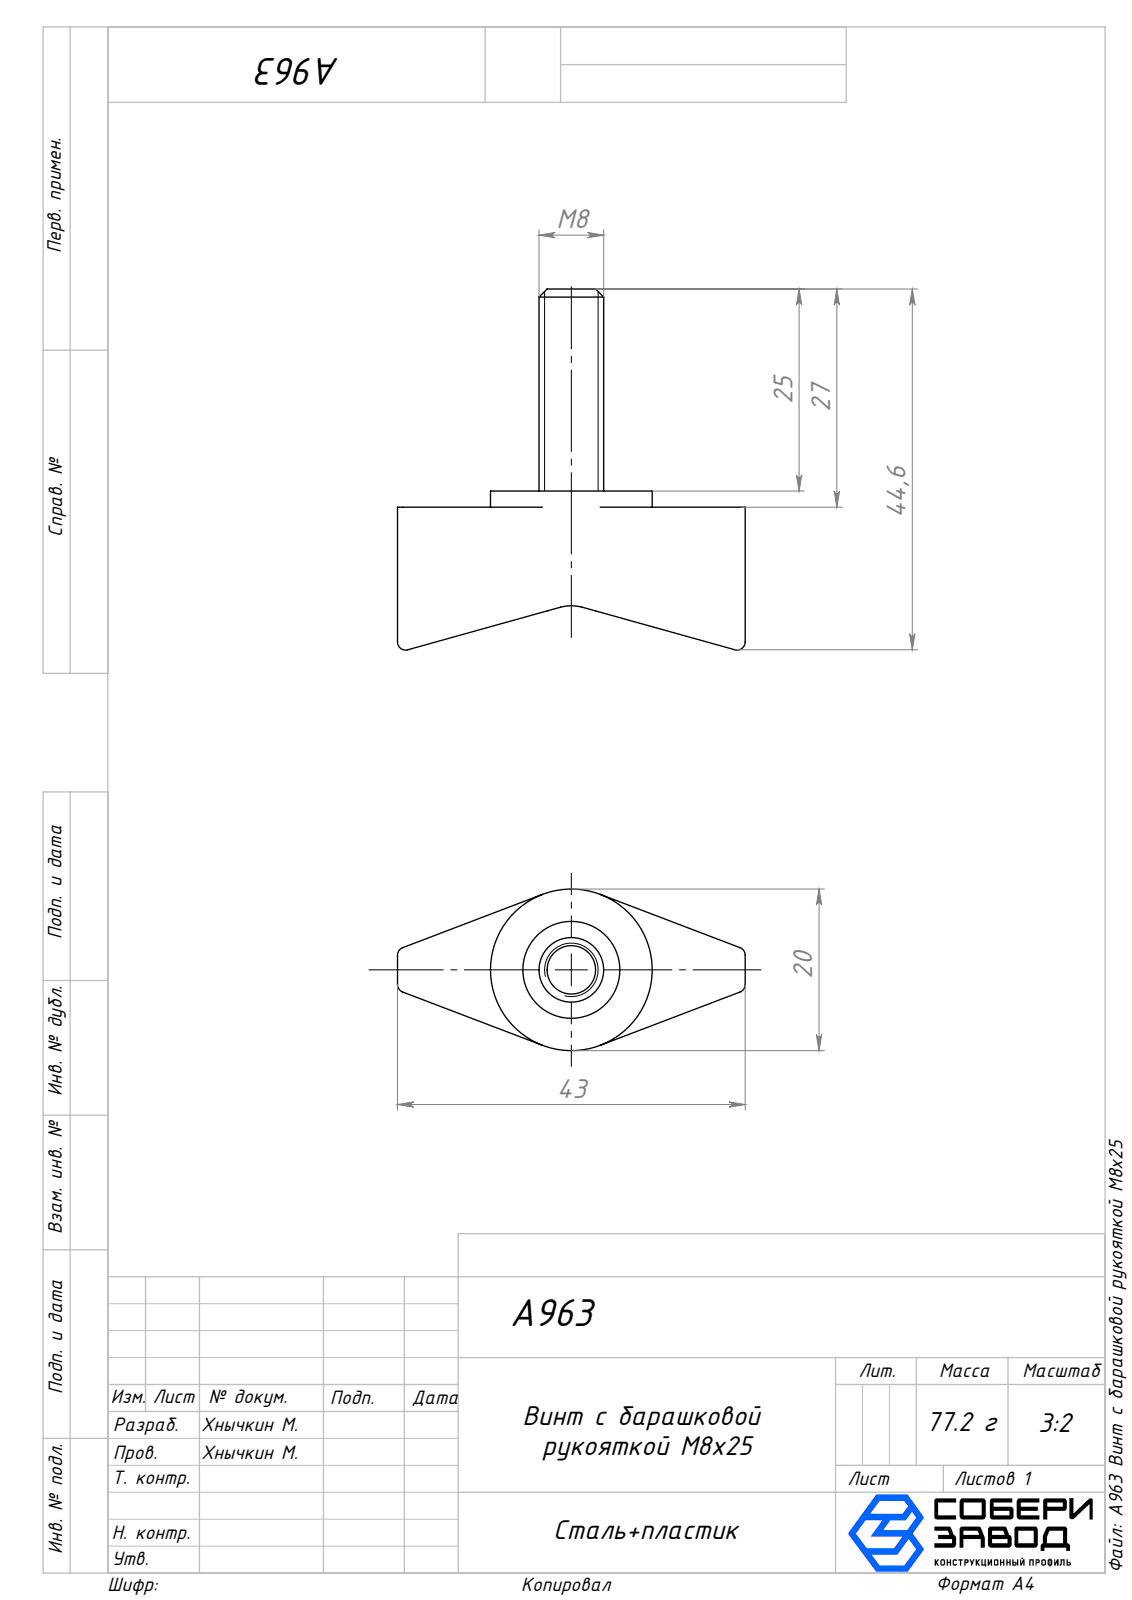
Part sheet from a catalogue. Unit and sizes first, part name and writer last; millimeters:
Units: millimetres
Overall size (bounding box): 44.68 × 43 × 20
Round holes (diameter × count): ⌀12 ×1
Round bosses / shafts (diameter × count): ⌀20 ×1, ⌀8 ×1
Partial cylindrical surfaces — rounded edges, fillets, slot ends (radius × count): R1 ×10, R5 ×1
Main face-to-face distances: 19.98, 2, 43, 25, 27
Volume: 9 839 mm³ · Surface area: 3 494 mm²
Bodies: 1 solid, 43 faces (13 planar, 18 cylindrical, 12 other)
Part name (STEP PRODUCT): A963 Винт с барашковой рукояткой М8х25
STEP written by: SolidWorks 2025 (AUTOMOTIVE_DESIGN)
